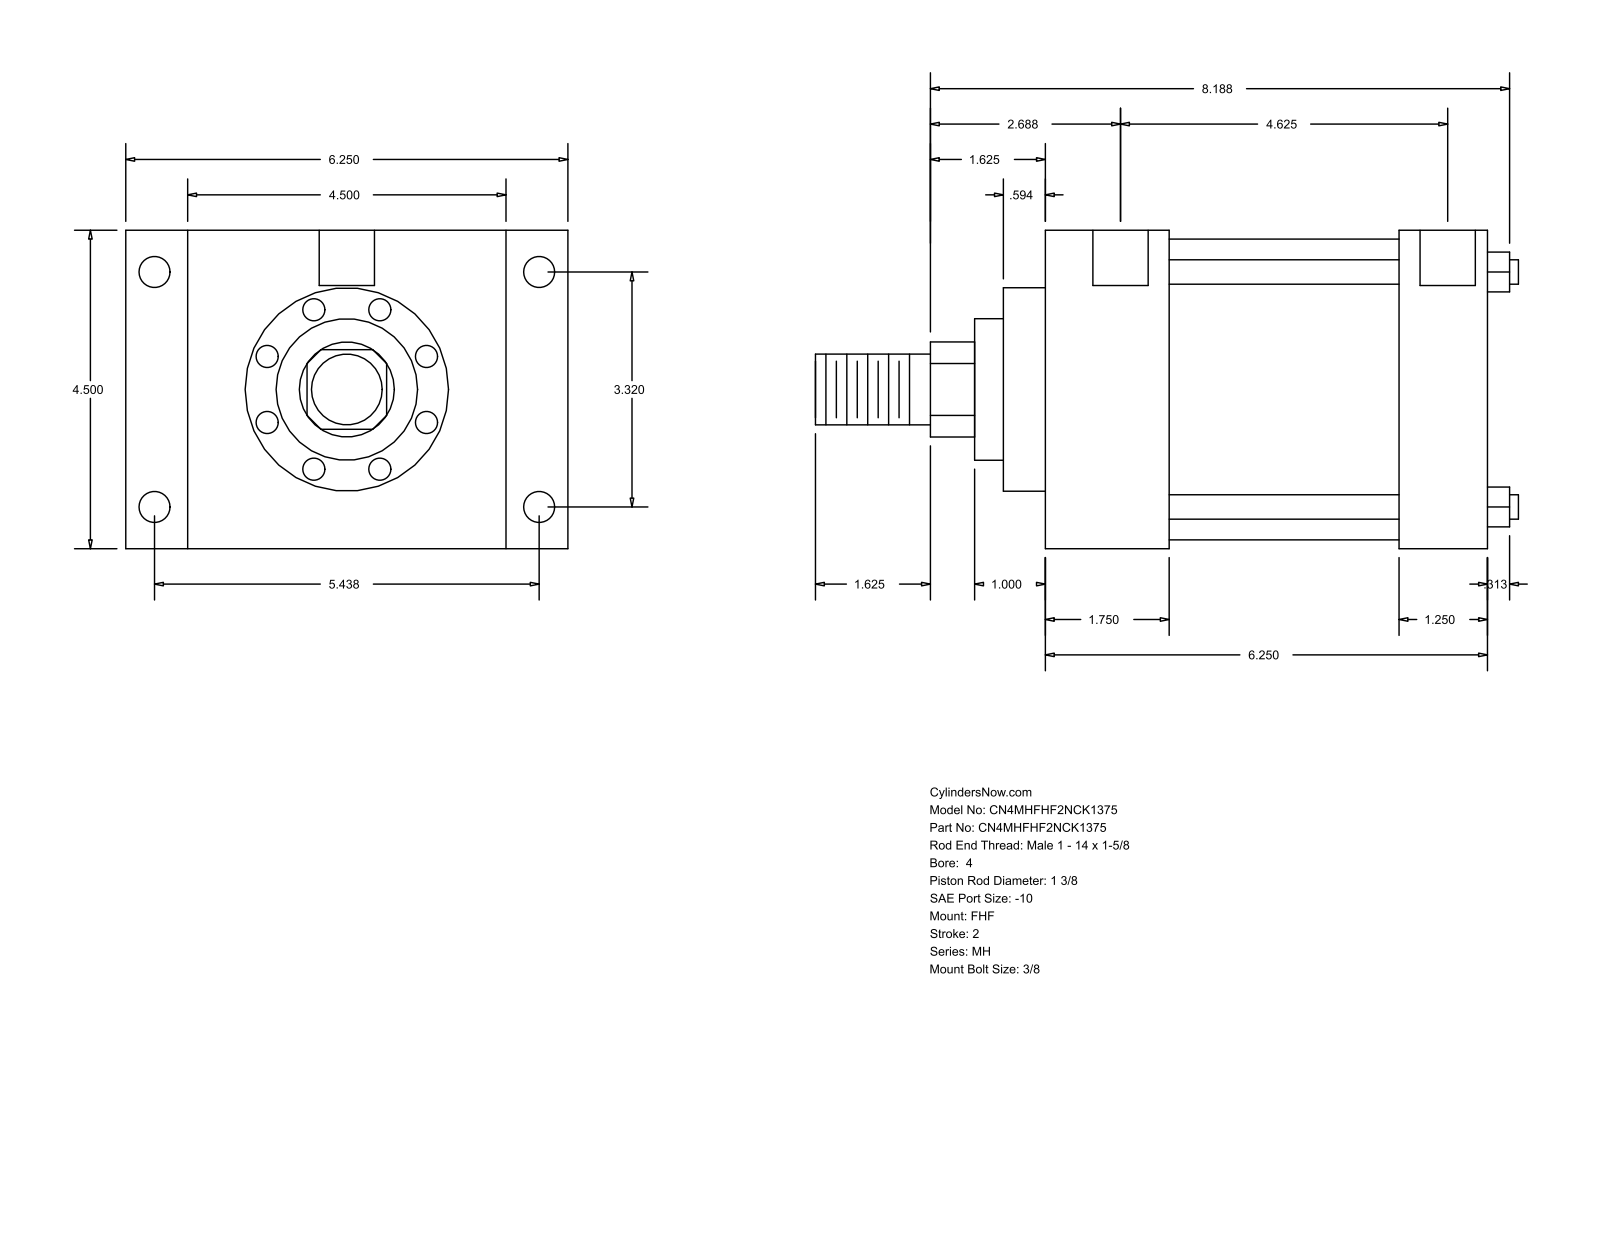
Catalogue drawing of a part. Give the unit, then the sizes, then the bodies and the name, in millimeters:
Units: millimetres
Overall size (bounding box): 252.41 × 158.75 × 114.3
Round holes (diameter × count): ⌀8.73 ×4, ⌀11.13 ×4, ⌀19.84 ×2
Round bosses / shafts (diameter × count): ⌀8.76 ×4, ⌀107.95 ×1, ⌀73.03 ×1, ⌀50.8 ×1, ⌀34.92 ×1, ⌀25.4 ×1
Partial cylindrical surfaces — rounded edges, fillets, slot ends (radius × count): R17.06 ×1
Main face-to-face distances: 158.76, 114.3, 44.45, 114.31, 22.23, 136.53, 127.01, 82.56, 31.75, 15.08
Hole centre spacings: 84.32, 120.65, 138.12, 161.82, 1.58, 1.59, 117.48, 119.06
Bodies: 0 solids, 90 faces (61 planar, 29 cylindrical, 0 other)
Part name (STEP PRODUCT): MH_FHF__0400_1.375
STEP written by: GSSL Pune (CONFIG_CONTROL_DESIGN)
